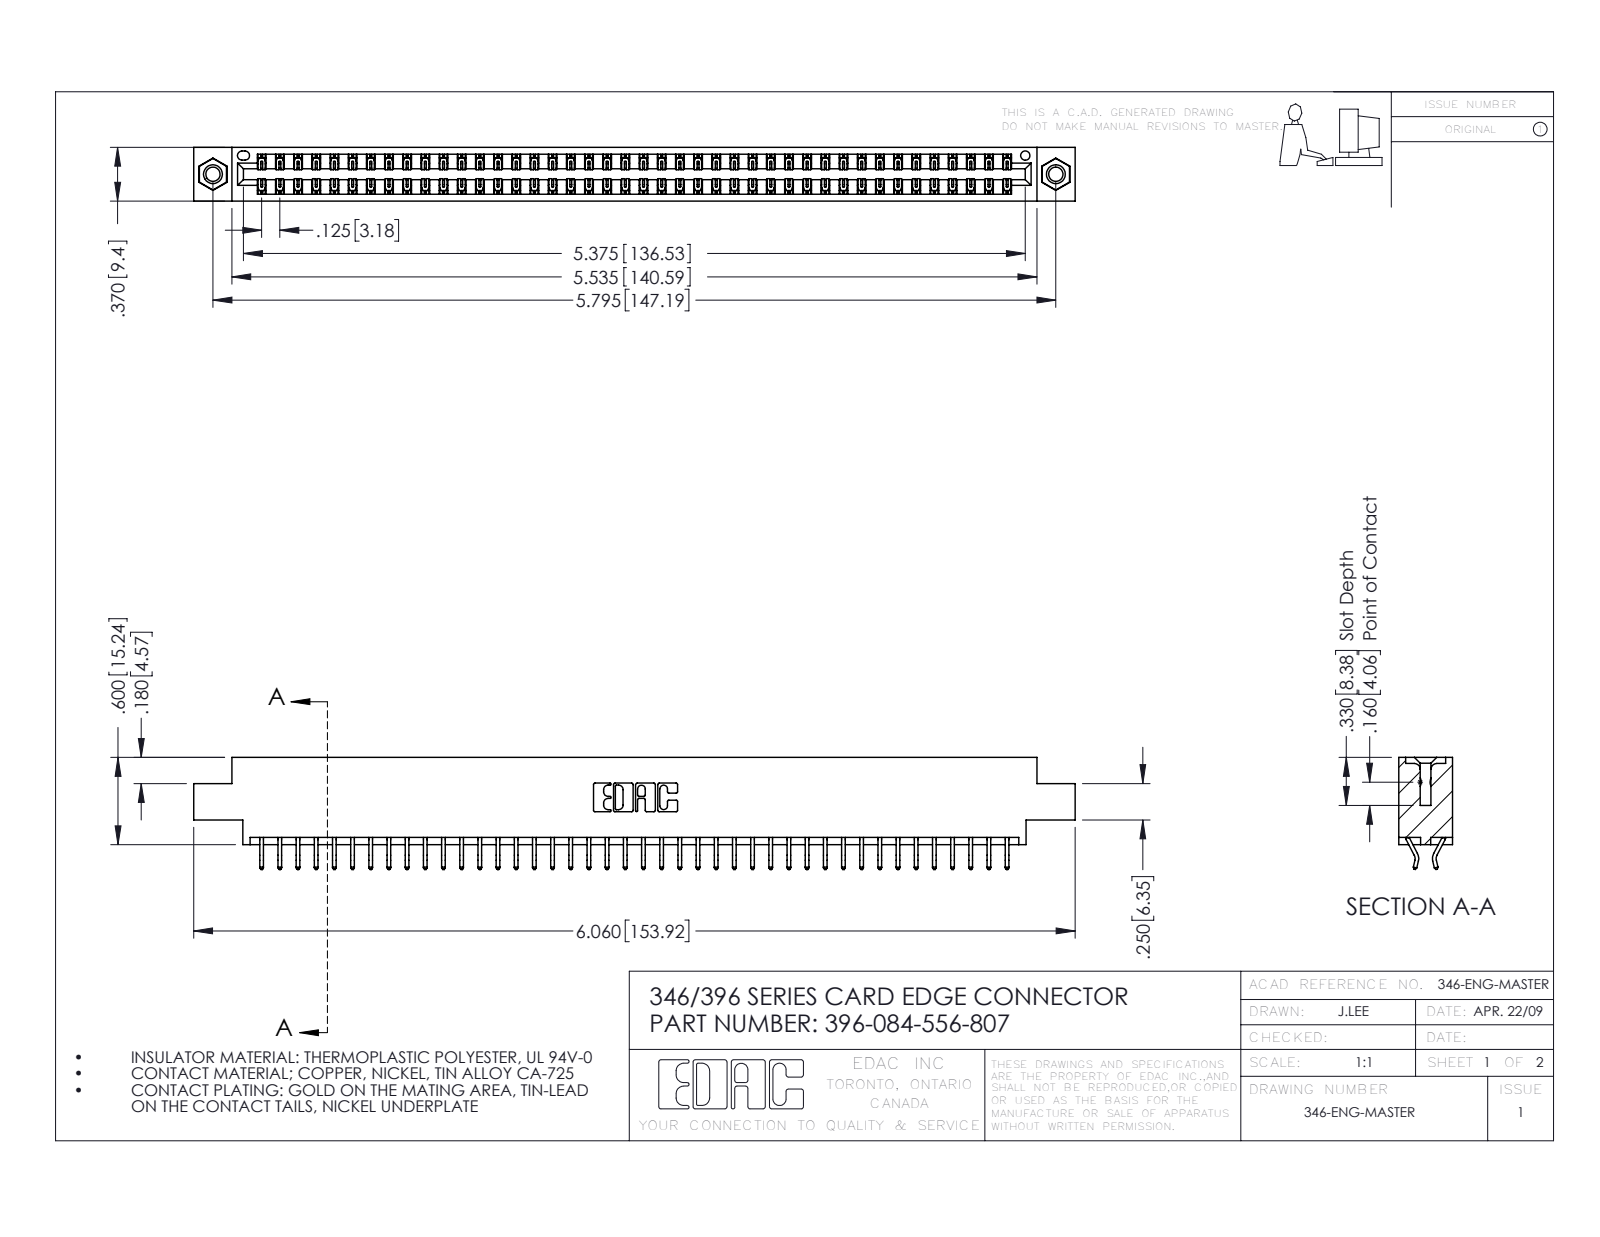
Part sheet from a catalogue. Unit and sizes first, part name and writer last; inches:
Units: inches
Overall size (bounding box): 6.06 × 0.77 × 0.37
Round holes (diameter × count): ⌀0.098 ×2, ⌀0.125 ×2, ⌀0.156 ×2, ⌀0.064 ×1
Round bosses / shafts (diameter × count): ⌀0.155 ×2
Partial cylindrical surfaces — rounded edges, fillets, slot ends (radius × count): R0.006 ×126, R0.01 ×22, R0.007 ×6, R0.031 ×6, R0.026 ×3, R0.01 ×2, R0.014 ×2, R0.022 ×2
Main face-to-face distances: 0.048, 0.322, 0.37, 0.25, 0.025, 0.072, 0.298, 0.275, 0.222, 0.148
Hole centre spacings: 0.246, 5.586, 5.795
Volume: 0.905 in³ · Surface area: 31.82 in²
Bodies: 87 solids, 5058 faces (3388 planar, 1654 cylindrical, 16 other)
Part name (STEP PRODUCT): 345-250-001_345-250-005-103; 346 Part_0.170 Offset - 0.156 Dia-TI; 345-292-001_556 Tail; 396-084-556-807
STEP written by: SolidWorks 2016 (CONFIG_CONTROL_DESIGN)
